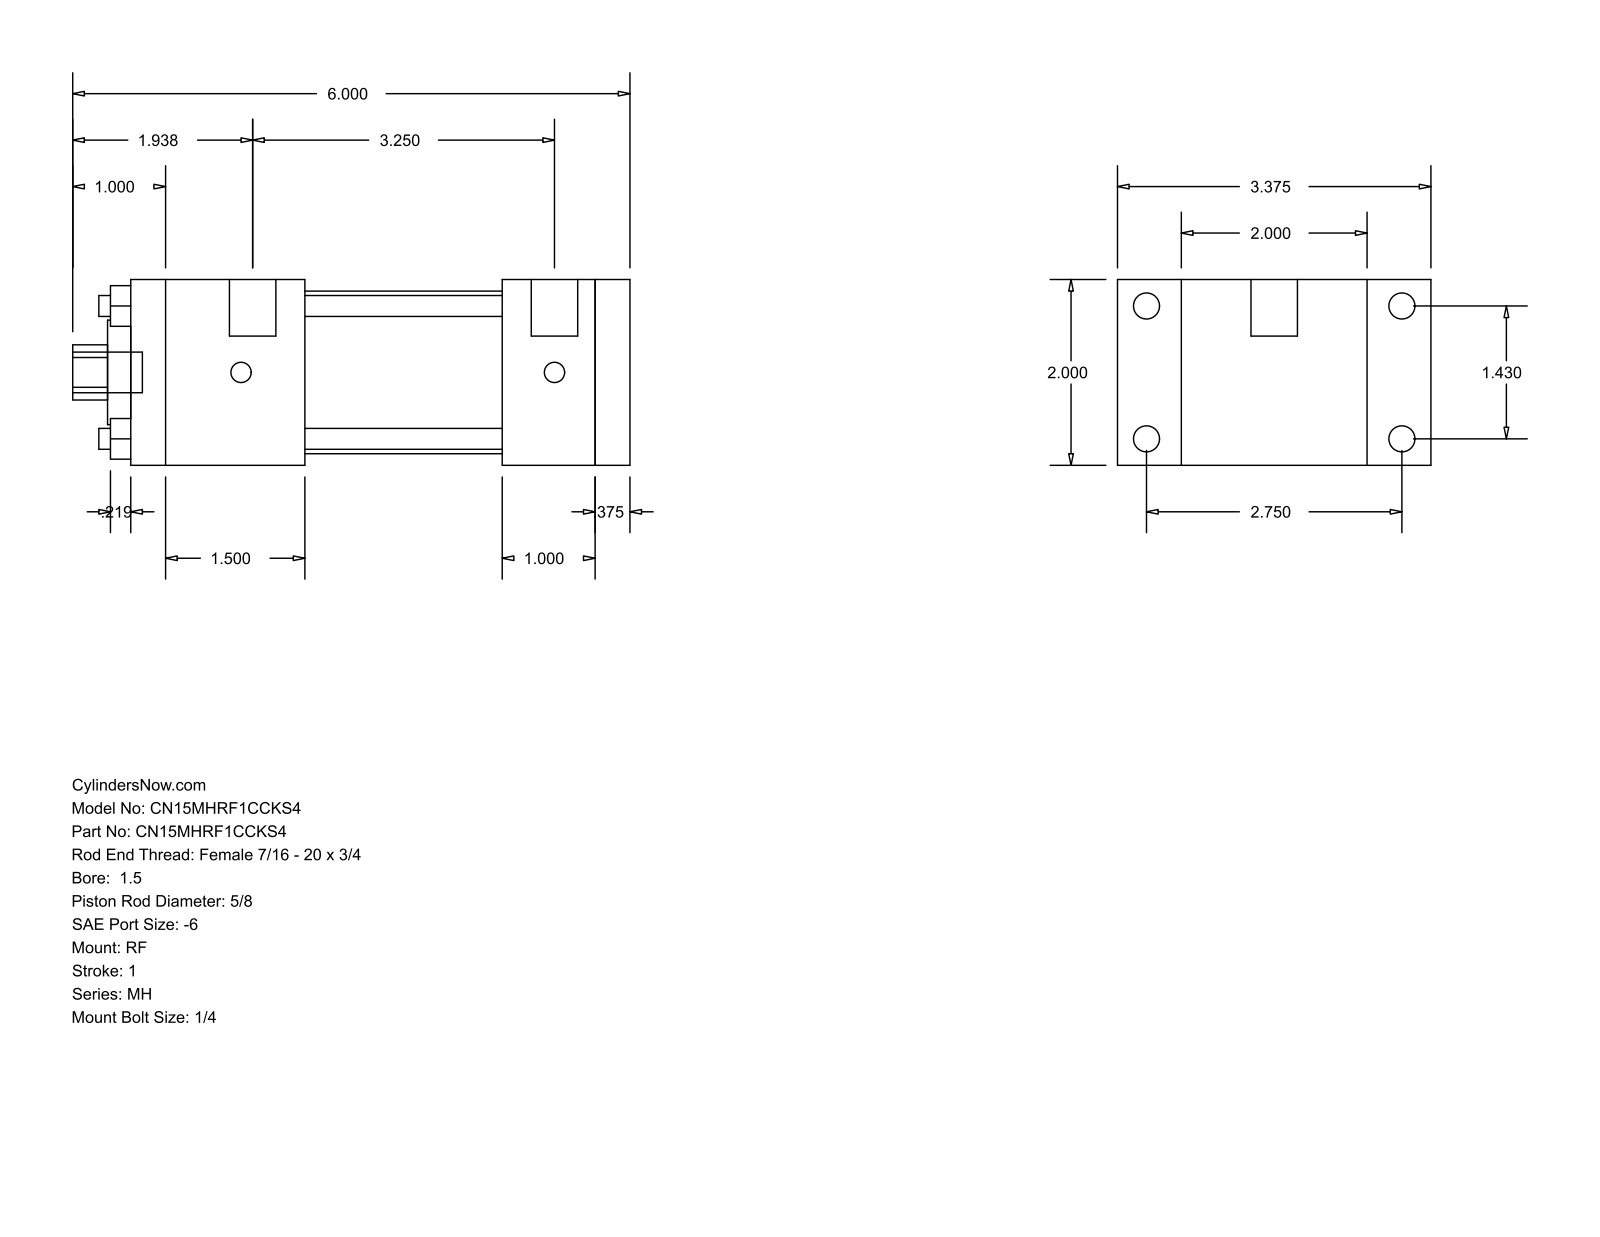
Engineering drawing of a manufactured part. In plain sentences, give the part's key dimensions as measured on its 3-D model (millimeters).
The part is named "MH_RF__0150_0.625". Its 3-D file was written by "GSSL Pune (CONFIG_CONTROL_DESIGN)". It is 0 solids with 92 faces: 64 planar, 28 cylindrical and 0 other. Overall it measures 152.4 by 85.72 by 50.8 millimeters. Round holes: 4 of diameter 5.71, 1 of diameter 15.88, 1 of diameter 28.57, 1 of diameter 44.45. Round bosses or shafts: 4 of diameter 7.14, 4 of diameter 5.56, 2 of diameter 12.7, 1 of diameter 11.11. Partial cylindrical surfaces (rounded edges, fillets, slot ends): 1 of radius 7.54. The main face-to-face distances are 50.8, 9.52, 127, 136.52, 53.97, 17.46, 68.26, 101.59, 25.41, 34.93. The hole center spacings are 25.68, 36.32, 51.36.
